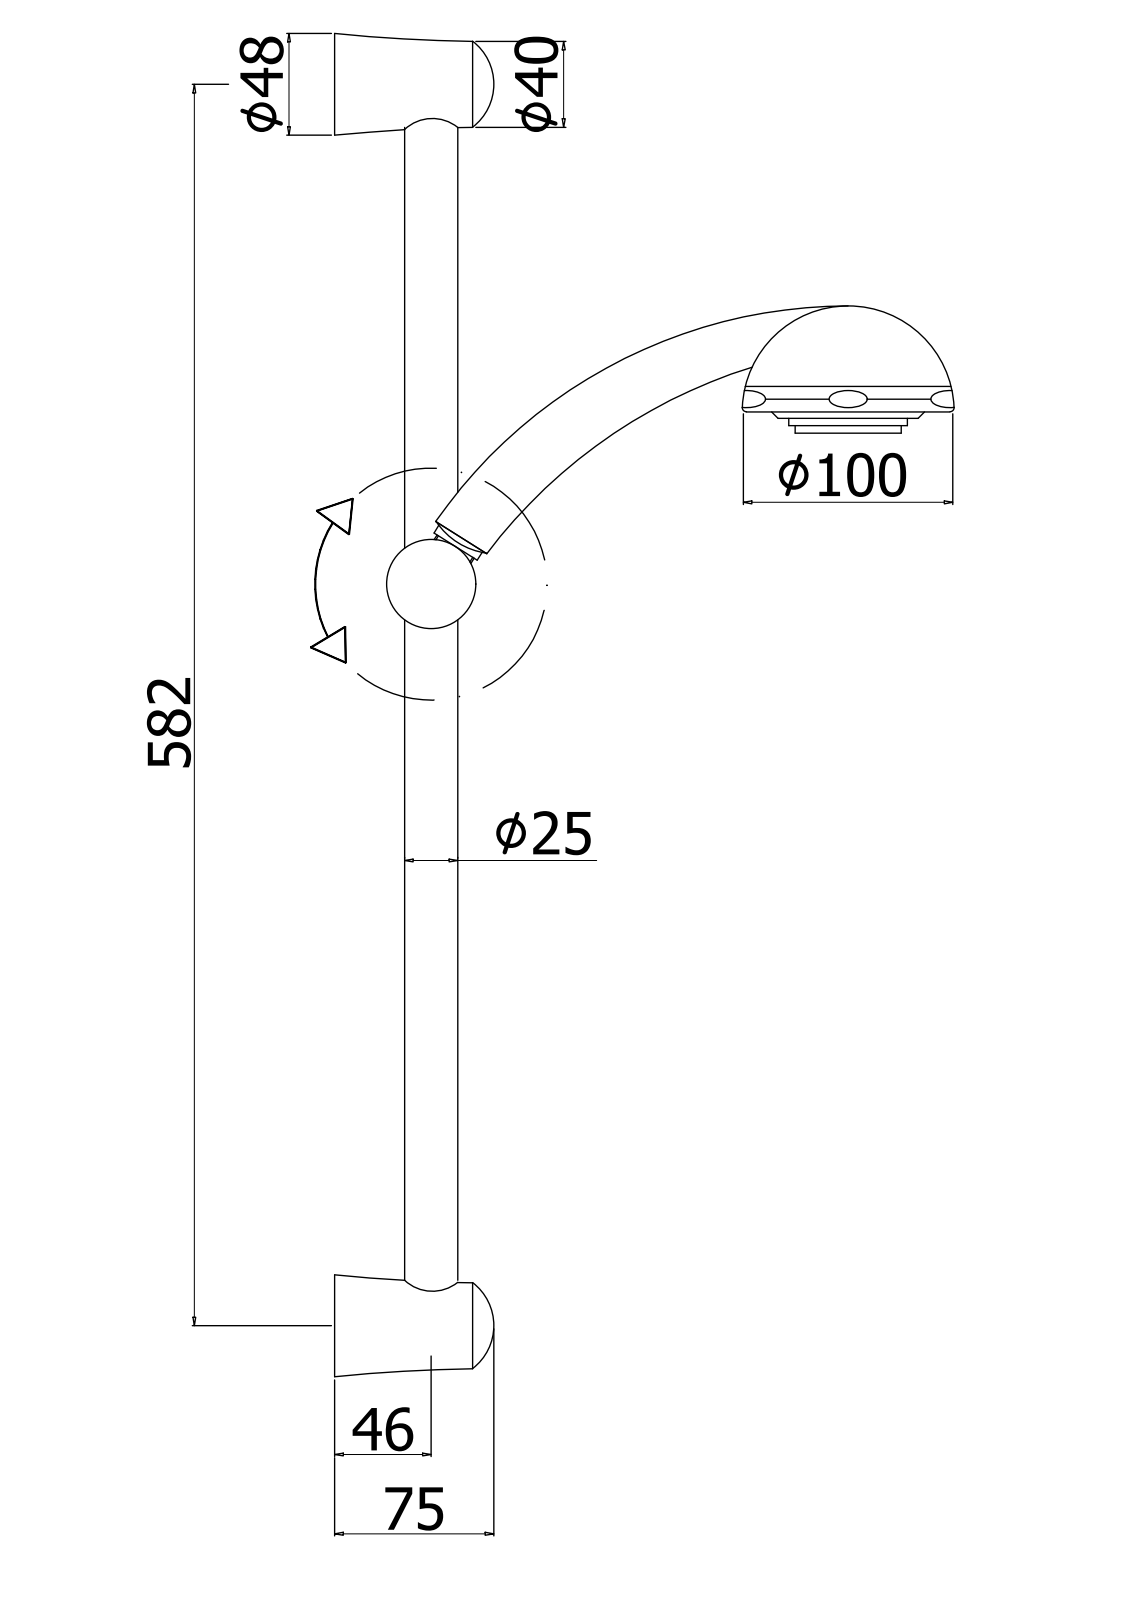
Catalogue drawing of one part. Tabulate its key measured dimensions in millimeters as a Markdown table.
| quantity | value |
| --- | --- |
| part name | 4071100CR; 4071003CRDG; 4071296CR_A; 4071296CR_B (+8 more) |
| STEP written by | CREO PARAMETRIC BY PTC INC, 2020044 (CONFIG_CONTROL_DESIGN) |
| units | millimeters |
| bodies | 16 solids, 1963 faces (417 planar, 528 cylindrical, 1018 other) |
| overall size | 630 × 264.86 × 153.14 |
| volume | 532 357 mm³ |
| surface area | 264 142 mm² |
| round holes (diameter × count) | 1.7 × 10, 4.2 × 10, 4.8 × 10, 2.8 × 4, 4.5 × 2, 3.5 × 1, 8 × 1, 9.75 × 1, 10 × 1, 11 × 1, 12 × 1, 14 × 1 |
| round bosses / shafts (diameter × count) | 3.4 × 40, 11 × 2, 91.5 × 1, 85.8 × 1, 85.2 × 1, 75.2 × 1, 72.3 × 1, 71 × 1 |
| partial cylindrical surfaces (radius × count) | 2.09 × 36, 0.3 × 16, 1 × 13, 2 × 12, 4 × 10, 2.6 × 8, 0.5 × 2, 3.5 × 2 |
| main face-to-face distances | 13.3, 2.5, 2.9, 2, 10.8, 12.8, 11, 8.4, 9.9, 3 |
| hole center spacings | 28.64, 11, 18.78, 19, 24.72, 12, 36.14, 30 |
